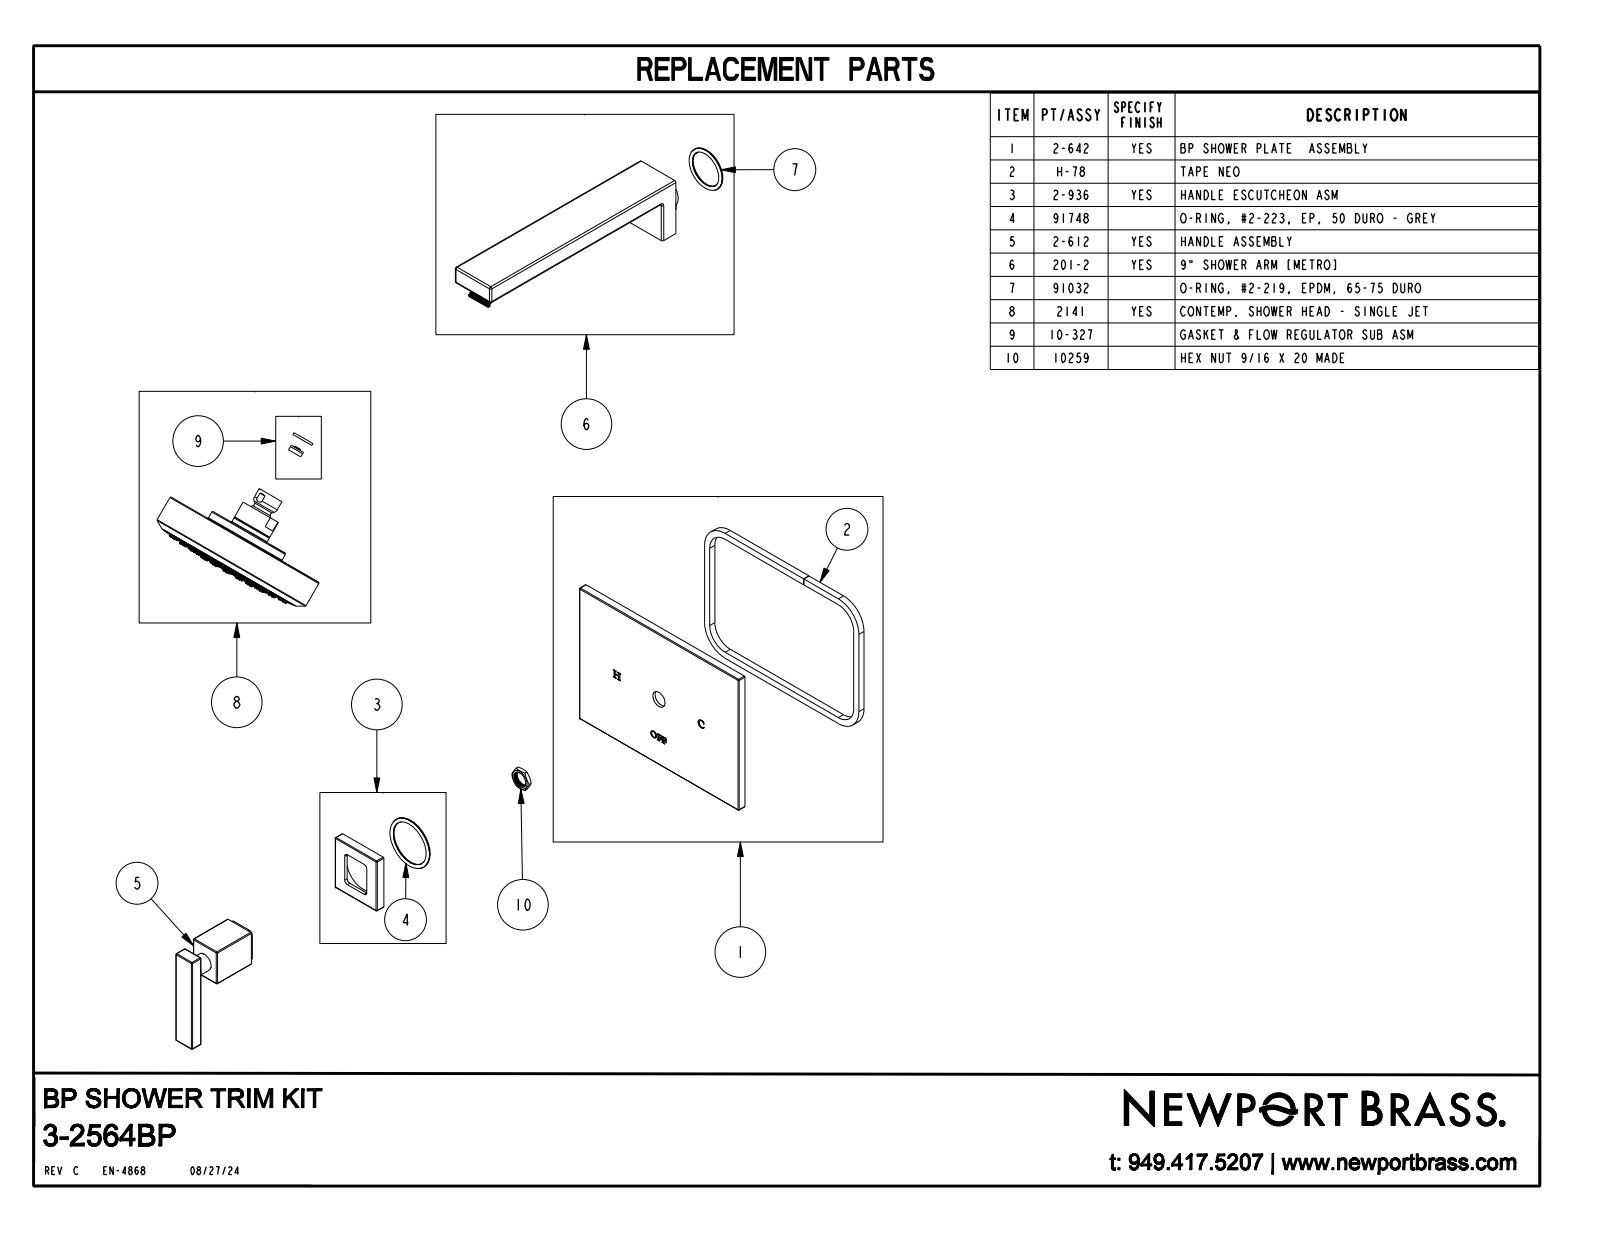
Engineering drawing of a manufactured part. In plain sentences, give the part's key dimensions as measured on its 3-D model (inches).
The part is named "3-2564BP". Its 3-D file was written by "CREO PARAMETRIC BY PTC INC, 2018400 (AUTOMOTIVE_DESIGN)". It is 64 solids with 1943 faces: 404 planar, 846 cylindrical and 693 other. Overall it measures 17.827 by 12.907 by 7.75 inches. Its volume is 36.38 cubic inches and its surface area 380.6 square inches. Round holes: 90 of diameter 0.05, 90 of diameter 0.125, 1 of diameter 0.22, 1 of diameter 0.526, 1 of diameter 0.59, 1 of diameter 0.604, 1 of diameter 0.917, 1 of diameter 1.01, 1 of diameter 1.25, 1 of diameter 4.9, 1 of diameter 5.256. Round bosses or shafts: 90 of diameter 0.198, 2 of diameter 1.4, 1 of diameter 5.91, 1 of diameter 5.22, 1 of diameter 5.1, 1 of diameter 2.92, 1 of diameter 1.75, 1 of diameter 1.1. Partial cylindrical surfaces (rounded edges, fillets, slot ends): 36 of radius 0.03, 24 of radius 0.125, 10 of radius 0.06, 4 of radius 0.532, 1 of radius 0.08, 1 of radius 0.475, 1 of radius 1.4. The main face-to-face distances are 0.11, 0.06, 0.796, 0.1, 0.896, 0.836, 0.736, 0.654, 0.291, 1.75. The hole center spacings are 1.84, 1.84, 2.27, 0.48, 0.952, 1.408, 3.648, 2.24.
